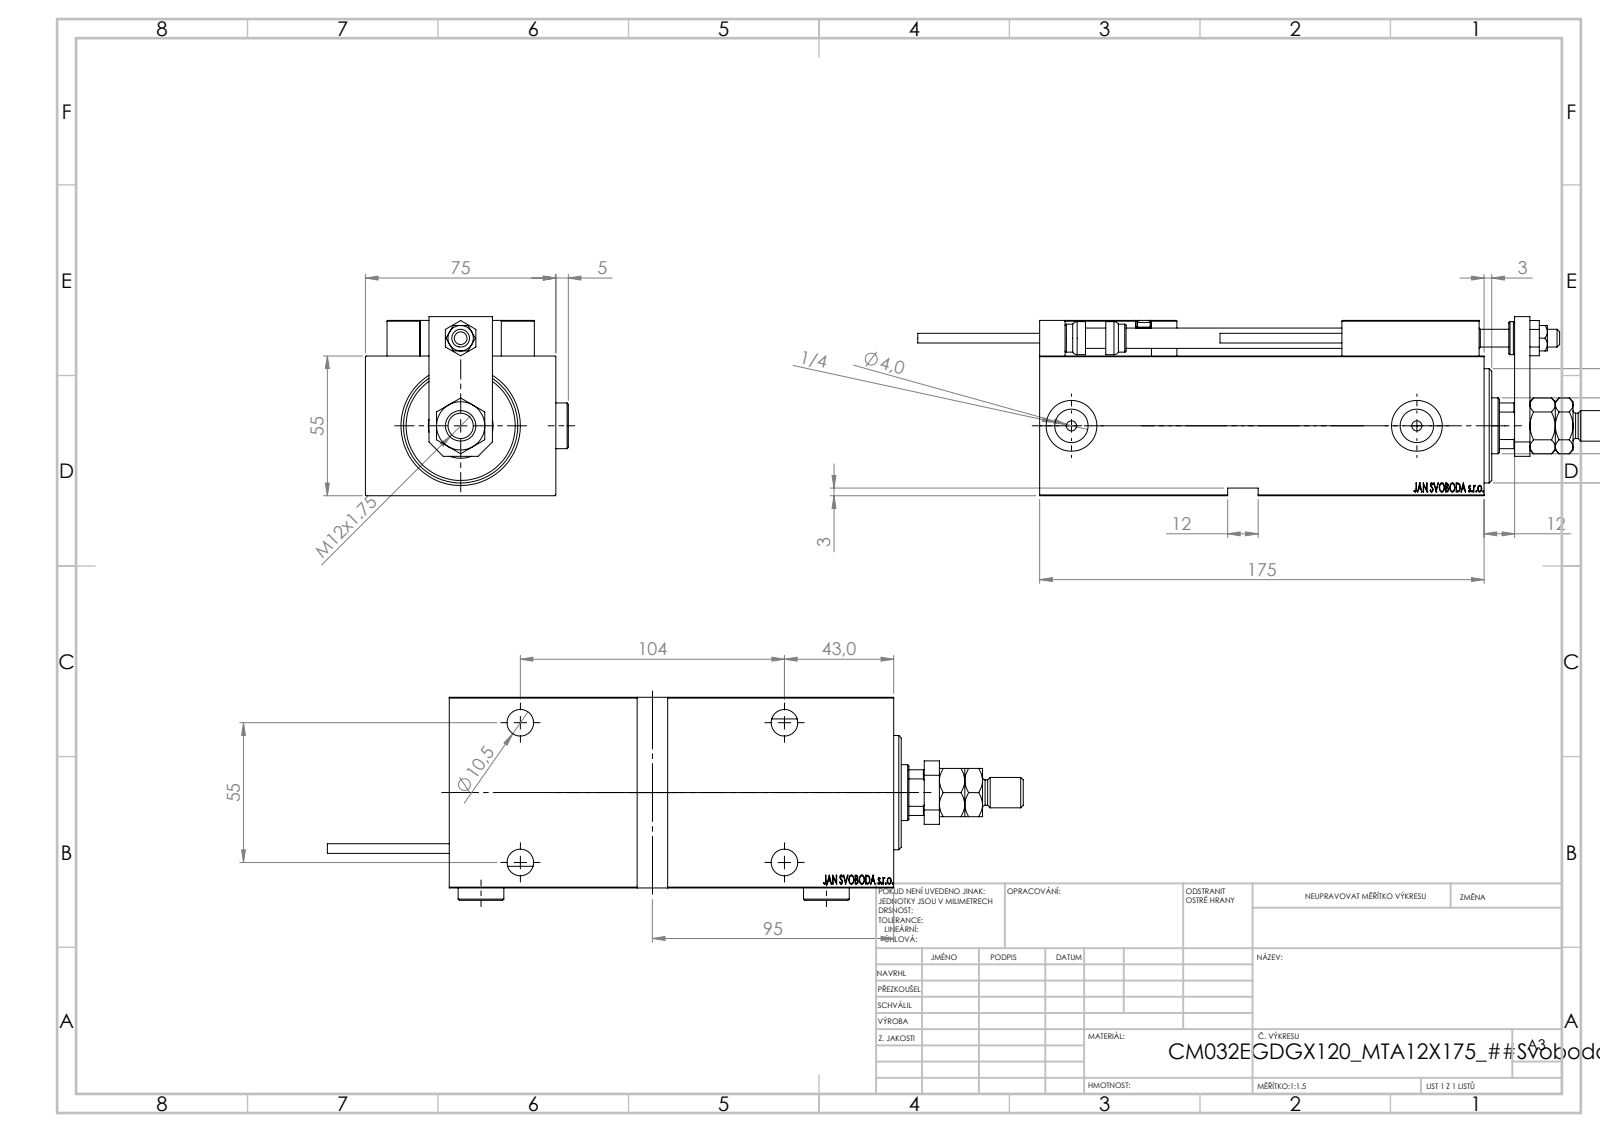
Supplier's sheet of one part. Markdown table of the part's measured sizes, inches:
| quantity | value |
| --- | --- |
| part name | V450CM_VC_B; V450CM_E_Body; ZARAZKA; ALLEN BOLT D5 (+7 more) |
| STEP written by | SolidWorks 2019 (CONFIG_CONTROL_DESIGN) |
| units | inches |
| bodies | 27 solids, 1395 faces (620 planar, 200 cylindrical, 575 other) |
| overall size | 10.787 × 3.146 × 2.776 |
| volume | 42.99 in³ |
| surface area | 207 in² |
| round holes (diameter × count) | 0.157 × 6, 0.315 × 5, 0.413 × 5, 0.65 × 5, 0.126 × 4, 0.197 × 2, 0.518 × 2, 0.787 × 2, 0.276 × 1, 0.866 × 1, 1.004 × 1, 1.26 × 1 |
| round bosses / shafts (diameter × count) | 0.709 × 2, 0.197 × 2, 0.15 × 2, 1.339 × 1, 0.512 × 1, 0.472 × 1, 0.433 × 1, 0.394 × 1 |
| partial cylindrical surfaces (radius × count) | 0.012 × 30, 0.118 × 2, 0.413 × 1 |
| main face-to-face distances | 2.165, 2.953, 0.118, 0.394, 0.551, 0.472, 6.89, 0.197, 2.717, 6.496 |
| hole center spacings | 0.448, 0.787, 1.138, 1.165, 1.169, 1.42, 1.576, 1.661 |
